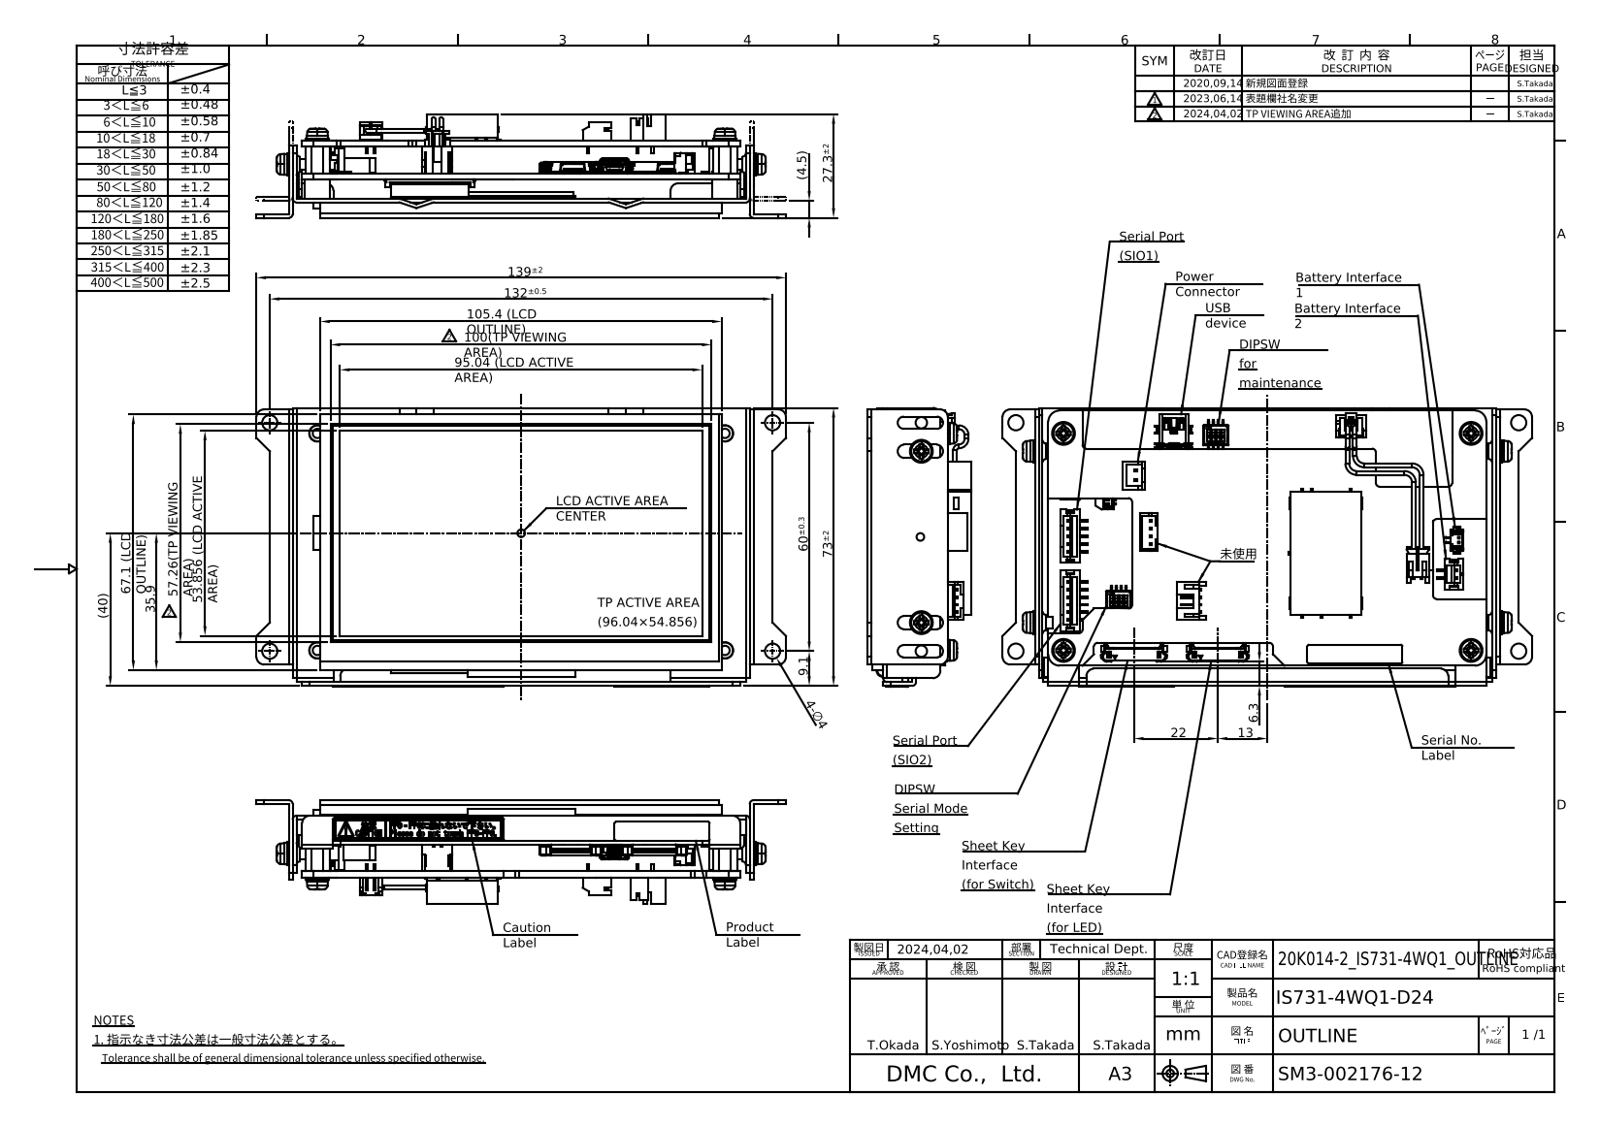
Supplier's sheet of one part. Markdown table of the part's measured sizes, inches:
| quantity | value |
| --- | --- |
| part name | HP_IS731-4WQ1-D24 |
| STEP written by | Autodesk Inventor 2020 (AUTOMOTIVE_DESIGN) |
| units | inches |
| bodies | 1 solid, 6109 faces (4610 planar, 852 cylindrical, 647 other) |
| overall size | 5.472 × 2.882 × 1.073 |
| volume | 4.554 in³ |
| surface area | 114.1 in² |
| round holes (diameter × count) | 0.157 × 6, 0.097 × 4, 0.138 × 4, 0.167 × 4, 0.047 × 2, 0.012 × 1, 0.052 × 1, 0.079 × 1 |
| round bosses / shafts (diameter × count) | 0.039 × 10, 0.118 × 8, 0.236 × 6, 0.217 × 6, 0.315 × 4, 0.256 × 4, 0.167 × 4, 0.146 × 3 |
| partial cylindrical surfaces (radius × count) | 0.004 × 116, 0.008 × 50, 0.012 × 48, 0.006 × 29, 0.039 × 21, 0.079 × 20, 0.005 × 16, 0.016 × 15 |
| main face-to-face distances | 0.063, 0.339, 0.26, 0.459, 0.199, 0.039, 0.197, 0.396, 0.276, 0.798 |
| hole center spacings | 0.492, 0.504, 2.244, 2.305, 2.362, 2.405, 4.213, 4.705 |
